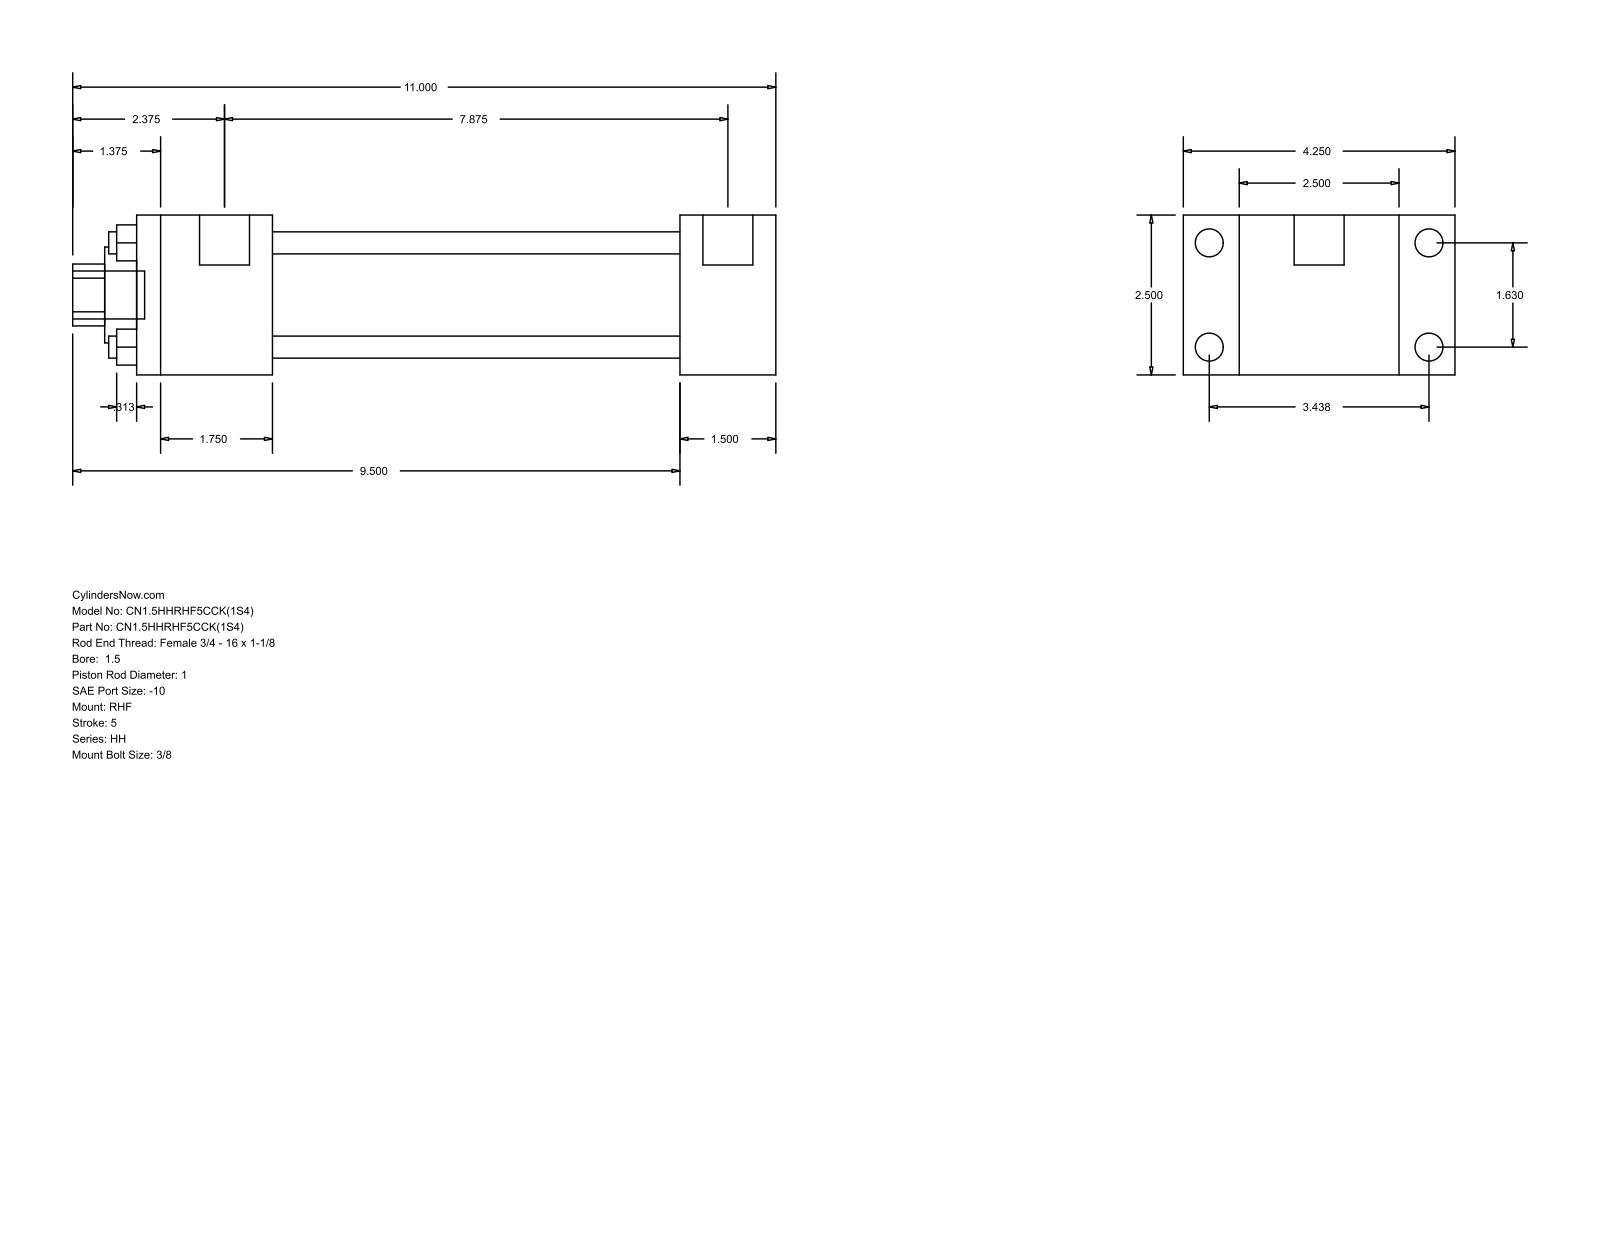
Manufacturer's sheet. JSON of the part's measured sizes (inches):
{"part_name": "HH_RHF__0150_1", "step_written_by": "GSSL Pune (CONFIG_CONTROL_DESIGN)", "units": "inches", "bodies": {"solids": 0, "faces": 88, "planar": 60, "cylindrical": 28, "other": 0}, "overall_size": [11, 4.25, 2.5], "round_holes": [[0.345, 4], [1, 1], [1.5, 1], [1.75, 1]], "round_bosses_or_shafts": [[0.438, 4], [0.219, 4], [0.781, 2], [0.75, 1]], "partial_cylinders_radius": [[0.484, 1]], "face_to_face_distances": [2.5, 0.875, 3.375, 1.5, 4.25, 6.375, 7.875, 2.125, 8.5, 10], "hole_center_spacings": [1.152, 1.63, 2.305]}
